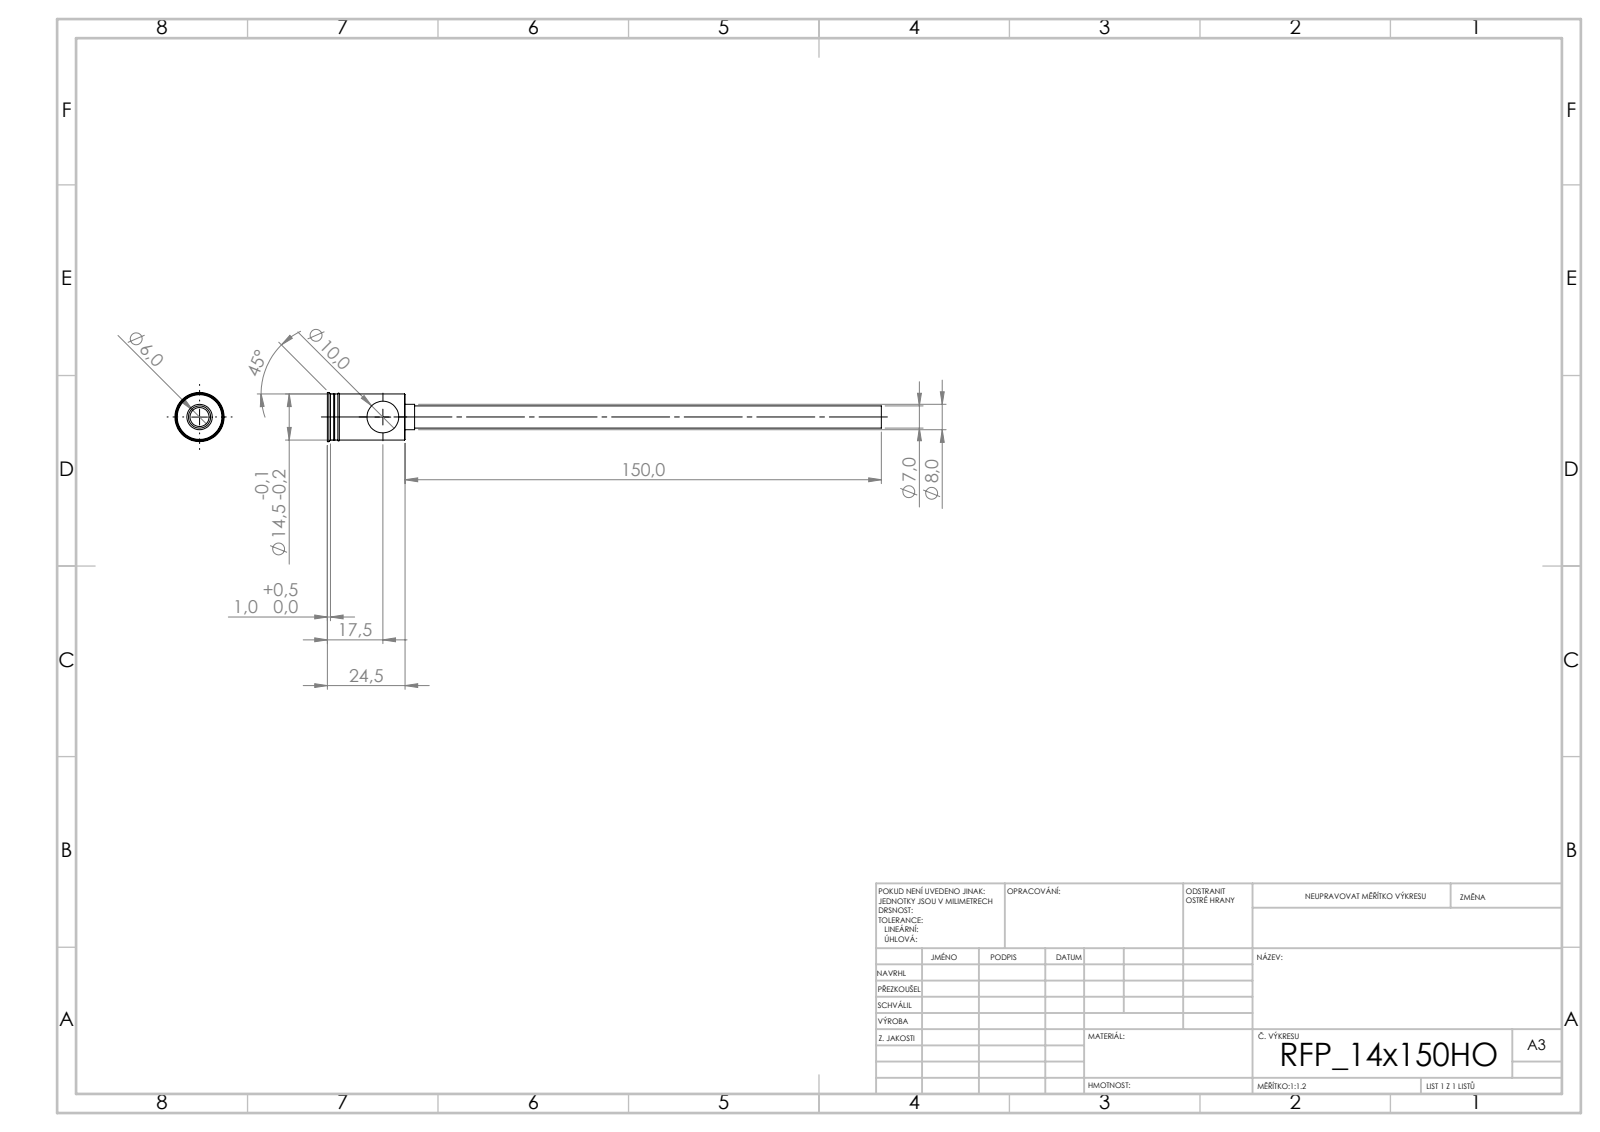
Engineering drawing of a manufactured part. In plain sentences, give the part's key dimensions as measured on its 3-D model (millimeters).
Its 3-D file was written by "SolidWorks 2019 (CONFIG_CONTROL_DESIGN)". It is 1 solid with 44 faces: 20 planar, 16 cylindrical and 8 other. Overall it measures 174.5 by 15.5 by 15.5 millimeters. Its volume is 4 333 cubic millimeters and its surface area 7 929 square millimeters. Round holes: 1 of diameter 6, 1 of diameter 10. Round bosses or shafts: 1 of diameter 15.5, 1 of diameter 14.5, 1 of diameter 8, 1 of diameter 7. The main face-to-face distances are 24.5, 22.5, 2, 9.9, 22.2, 2.3, 3, 25.2, 25.5, 27.5.
